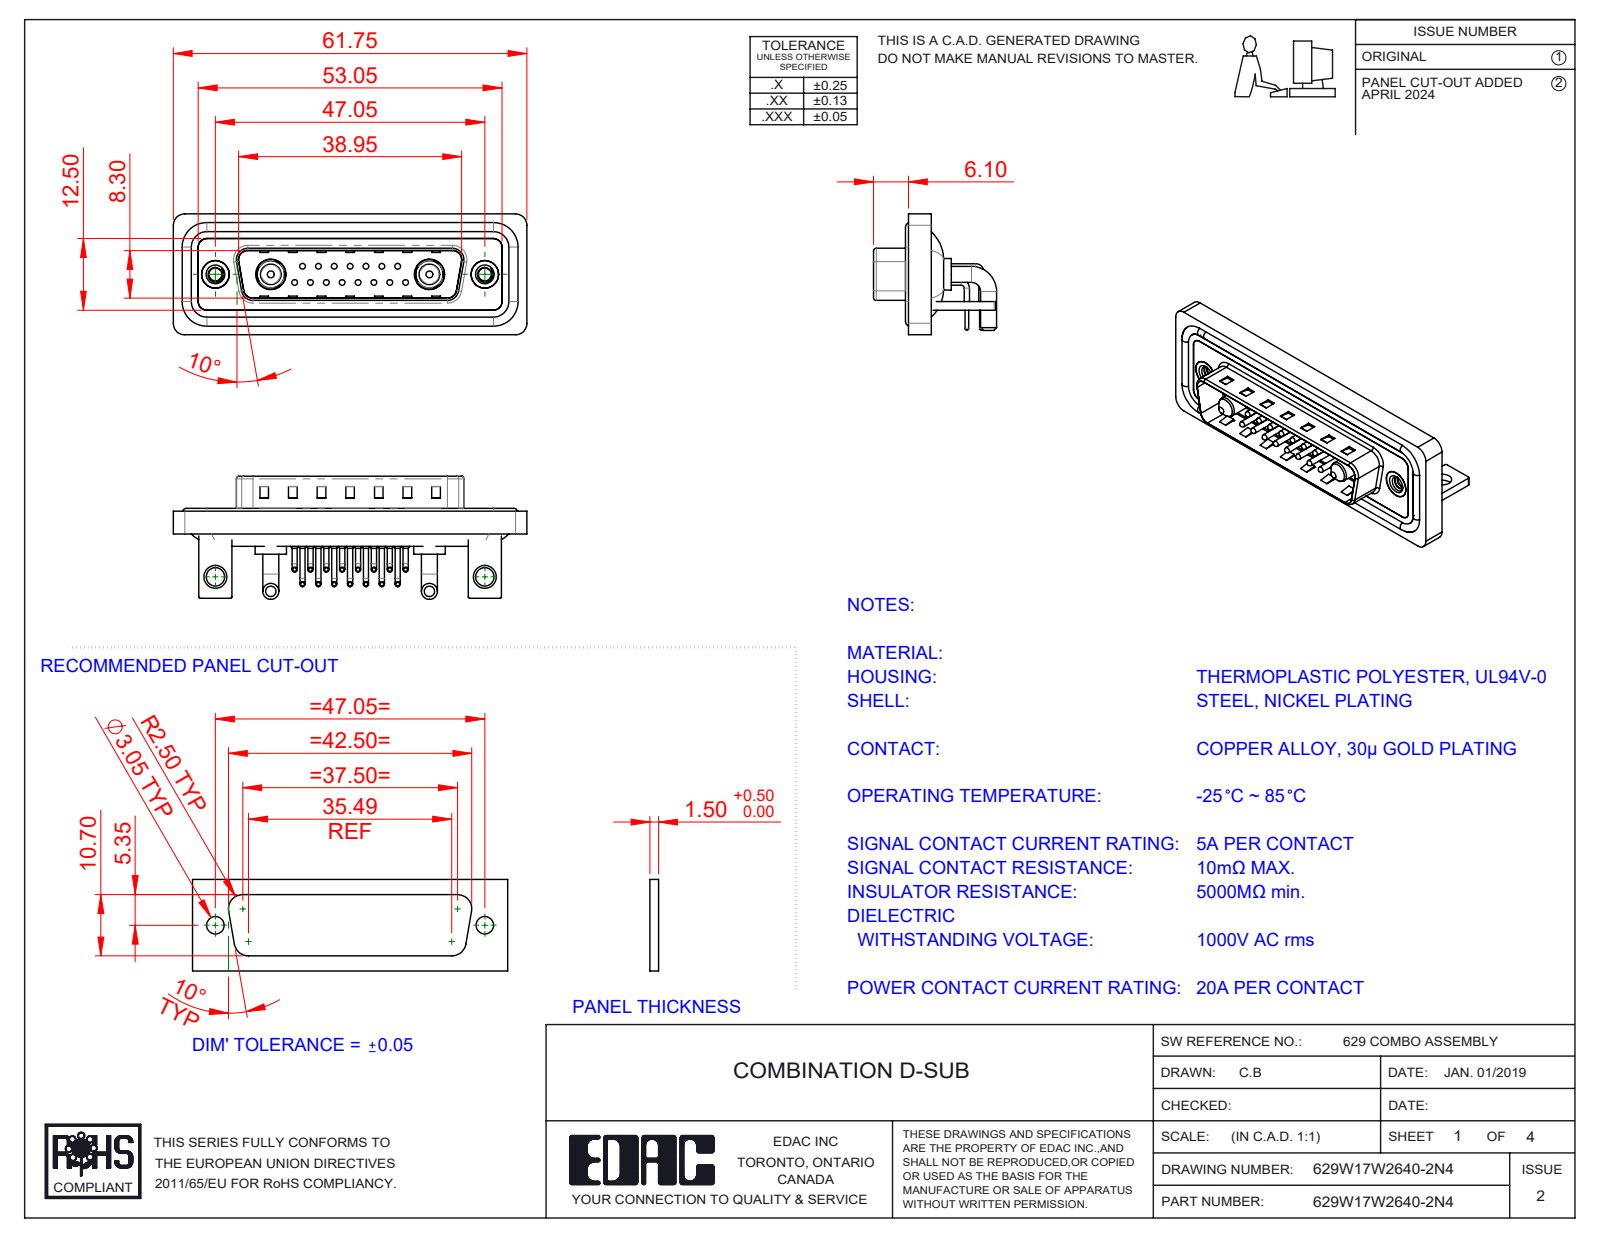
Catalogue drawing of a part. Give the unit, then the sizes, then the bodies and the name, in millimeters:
Units: millimetres
Overall size (bounding box): 61.75 × 21.5 × 21.1
Round holes (diameter × count): ⌀0.75 ×15, ⌀1.6 ×15, ⌀2 ×15, ⌀2.26 ×2, ⌀3.2 ×2, ⌀4 ×2, ⌀4.8 ×2, ⌀4.85 ×2, ⌀5 ×2, ⌀5.3 ×2
Round bosses / shafts (diameter × count): ⌀0.9 ×30, ⌀1.5 ×15, ⌀1 ×15, ⌀0.65 ×15, ⌀2.8 ×4, ⌀1.6 ×4, ⌀5.5 ×2, ⌀5.2 ×2
Partial cylindrical surfaces — rounded edges, fillets, slot ends (radius × count): R2 ×19, R1.5 ×18, R0.25 ×16, R1.01 ×15, R0.5 ×9, R1.6 ×8, R0.6 ×4, R0.65 ×4
Main face-to-face distances: 0.4, 0.8, 1.5, 2.1, 2.9, 1.1, 4.1, 1.6, 4.5, 3.7
Hole centre spacings: 3.16, 2.77, 5.54, 8.31, 5.04, 7.49, 11.08, 5.03
Volume: 7 790 mm³ · Surface area: 13 188 mm²
Bodies: 28 solids, 2259 faces (1209 planar, 788 cylindrical, 262 other)
Part name (STEP PRODUCT): 629Combo Shell Front_25 Contacts; 629Combo Waterproof Housing_25 Contacts; 629Combo Threaded Rivet_3; 629Combo Contact Row 1 (+6 more)
STEP written by: SolidWorks 2023 (CONFIG_CONTROL_DESIGN)
